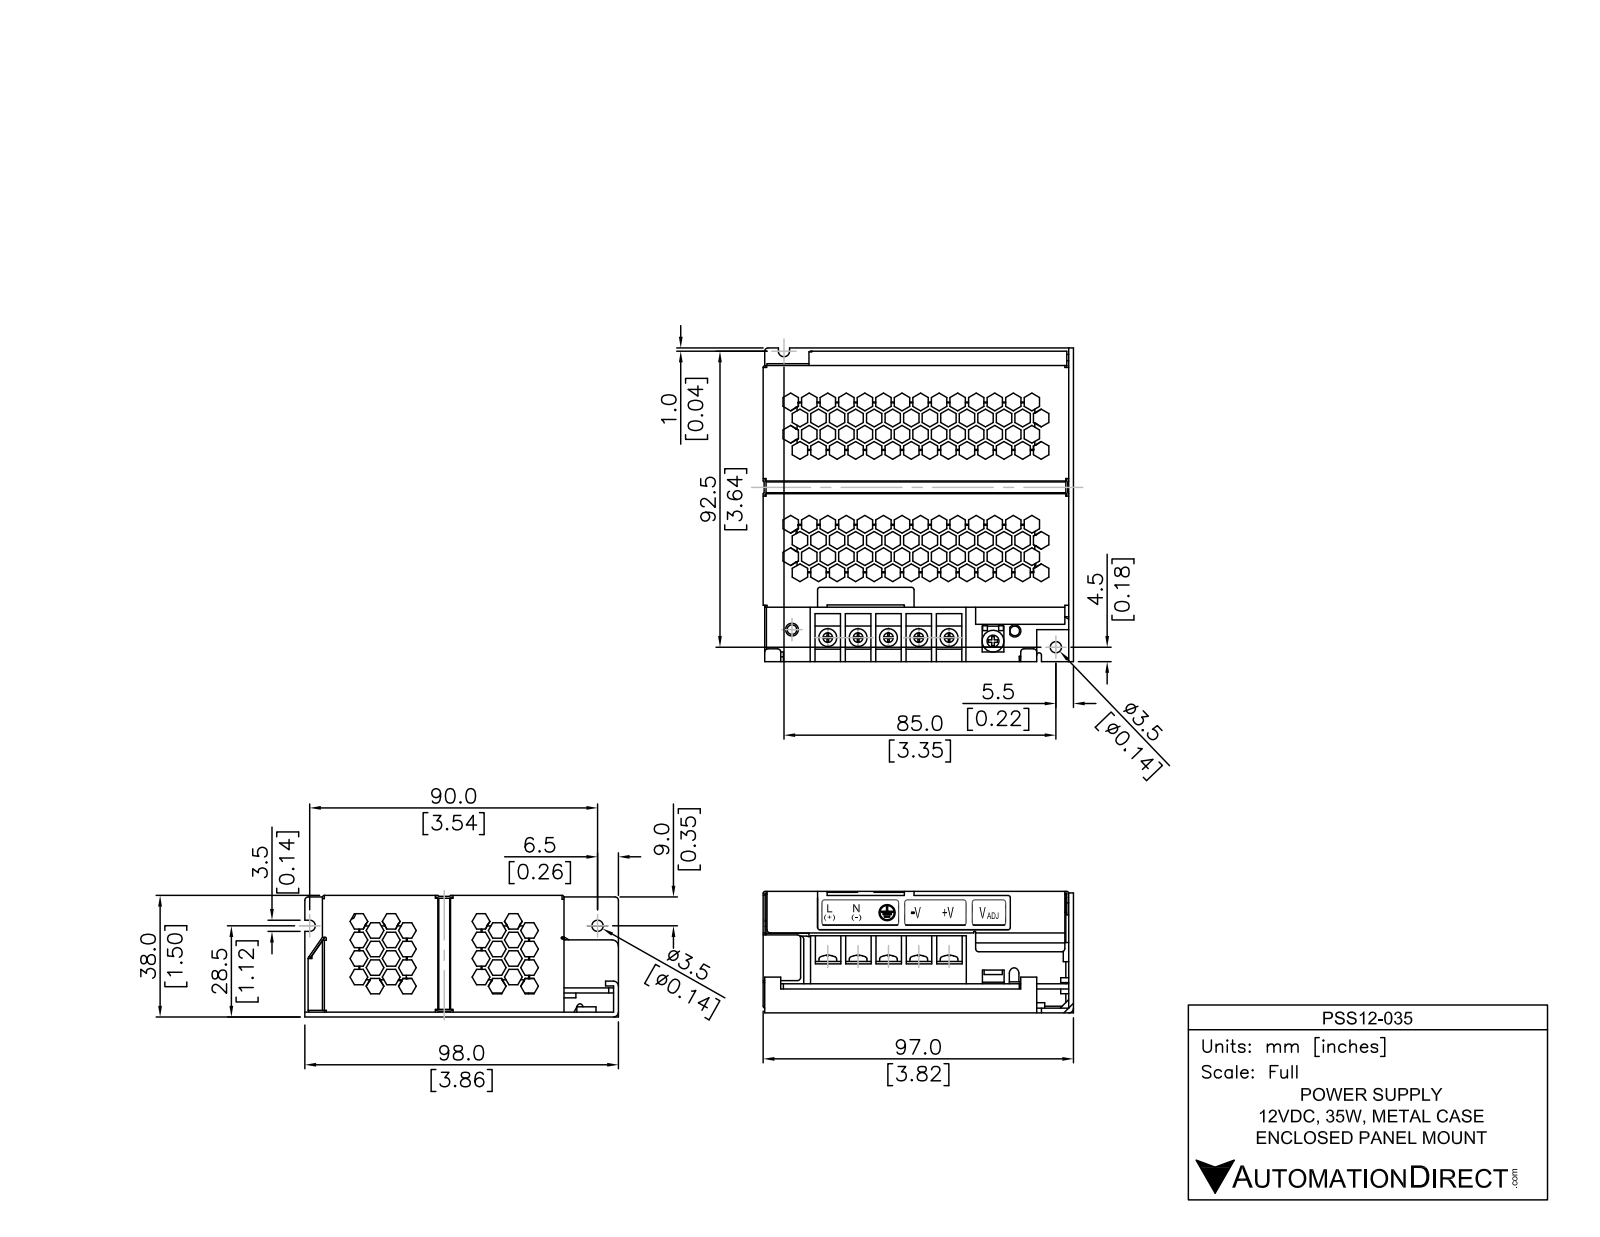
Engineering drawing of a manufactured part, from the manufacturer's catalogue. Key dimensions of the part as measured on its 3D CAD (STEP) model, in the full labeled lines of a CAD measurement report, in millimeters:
Part name (STEP PRODUCT): PSS 12-035
STEP written by: SolidWorks 2011 (CONFIG_CONTROL_DESIGN)
Units: millimetres
Bodies: 2 solids, 1245 faces (1124 planar, 59 cylindrical, 62 other)
Overall size (bounding box): 98 × 97 × 38.1
Volume: 128 000 mm³ · Surface area: 80 650 mm²
Round holes (diameter × count): ⌀3.3 ×2
Round bosses / shafts (diameter × count): ⌀5.6 ×5, ⌀7 ×1, ⌀3.1 ×1
Partial cylindrical surfaces — rounded edges, fillets, slot ends (radius × count): R0.8 ×7, R1 ×5, R1.3 ×5, R1.5 ×4, R0.4 ×2, R1.8 ×2, R4.4 ×2, R2.5 ×1
Main face-to-face distances: 0.8, 37.3, 8.3, 9.8, 36.6, 27.6, 7.5, 1.5, 1.5, 9
